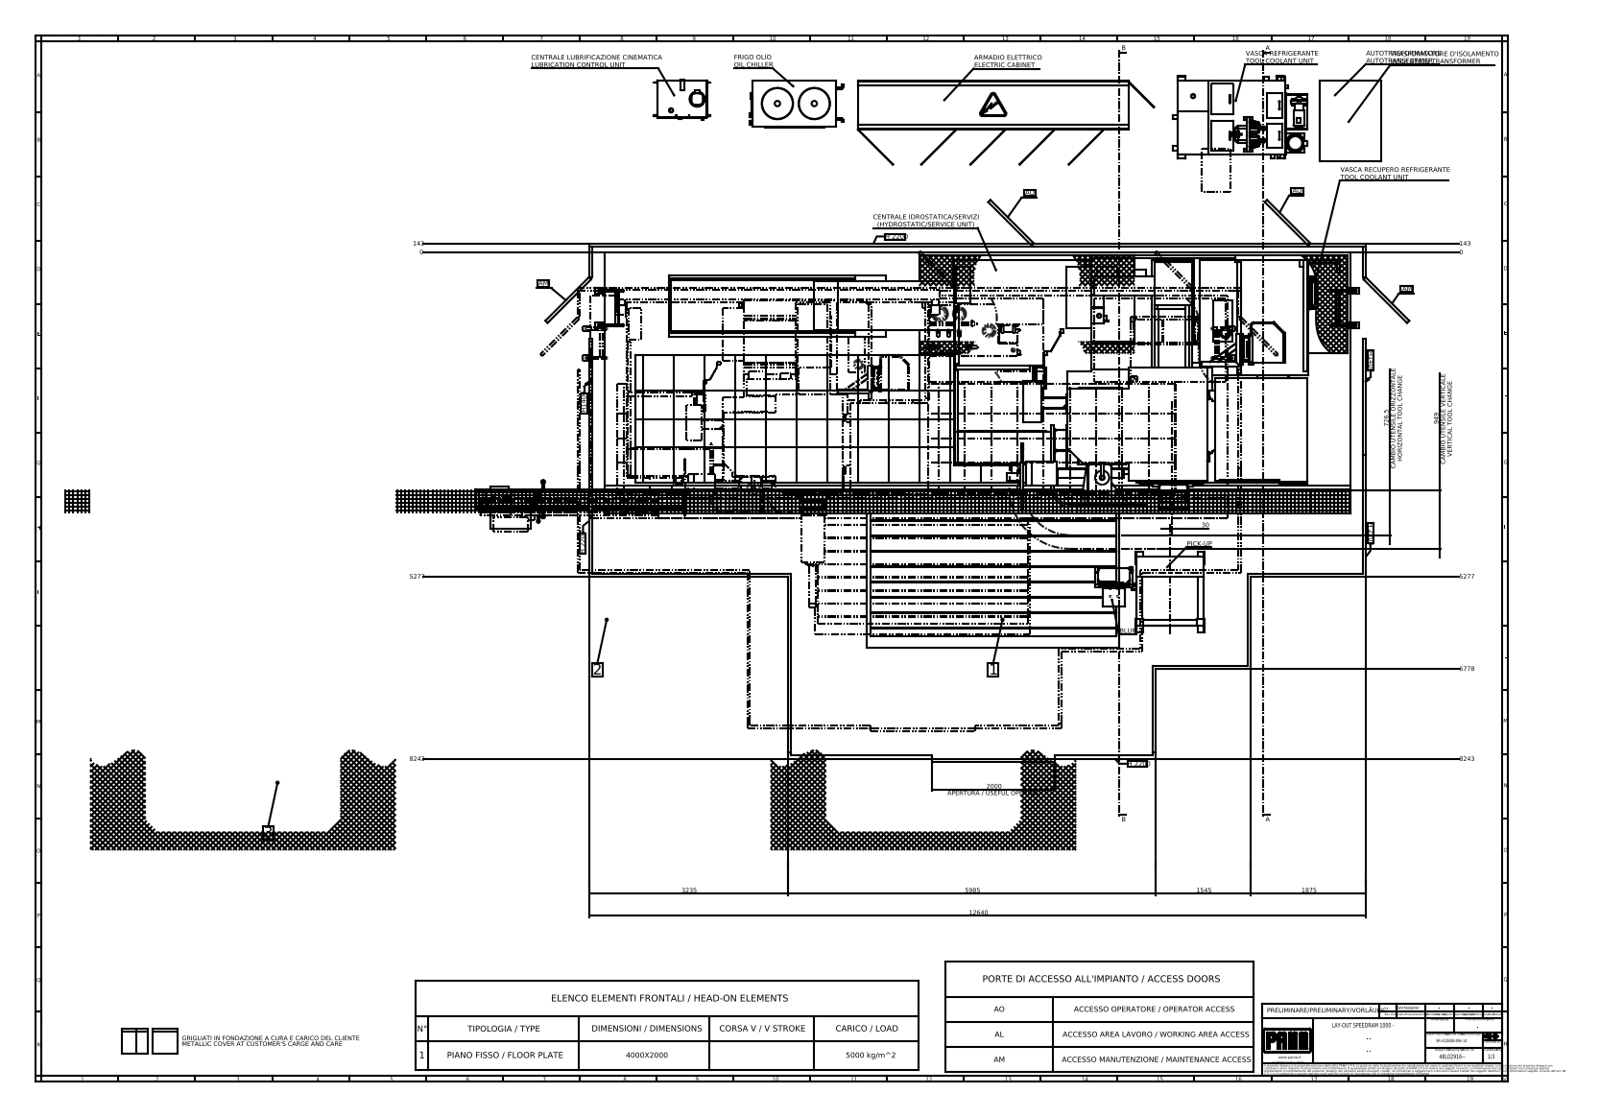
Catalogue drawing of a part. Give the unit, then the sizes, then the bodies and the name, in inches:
Units: inches
Overall size (bounding box): 635.433 × 553.441 × 311.516
Round holes (diameter × count): ⌀1.378 ×64, ⌀2.74 ×63, ⌀1.465 ×18, ⌀1.181 ×9, ⌀0.512 ×8, ⌀0.551 ×8, ⌀0.315 ×6, ⌀0.492 ×4, ⌀2.231 ×4, ⌀2.362 ×4, ⌀1.008 ×3, ⌀1.969 ×3
Round bosses / shafts (diameter × count): ⌀1.669 ×18, ⌀0.787 ×14, ⌀1.575 ×11, ⌀0.354 ×10, ⌀2.165 ×8, ⌀2.61 ×7, ⌀2.362 ×6, ⌀1.378 ×6
Partial cylindrical surfaces — rounded edges, fillets, slot ends (radius × count): R0.197 ×128, R0.591 ×53, R0.315 ×52, R1.378 ×26, R0.236 ×25, R0.118 ×21, R0.157 ×21, R0.394 ×20
Main face-to-face distances: 78.74, 1.969, 49.094, 29.646, 0.197, 0.394, 550.63, 635.433, 104.331, 106.299
Hole centre spacings: 10.753, 19.685, 48.644, 29.843, 56.047, 39.37, 5.118, 10.236
Volume: 25 140 000 in³ · Surface area: 2 482 000 in²
Bodies: 401 solids, 6304 faces (4429 planar, 1421 cylindrical, 454 other)
Part name (STEP PRODUCT): S001568_1000 L; S003390; S003193_X=5000; S003241_Z=1200; BASAM.1400 (+8 more)
STEP written by: SolidWorks 2023 (AUTOMOTIVE_DESIGN)
